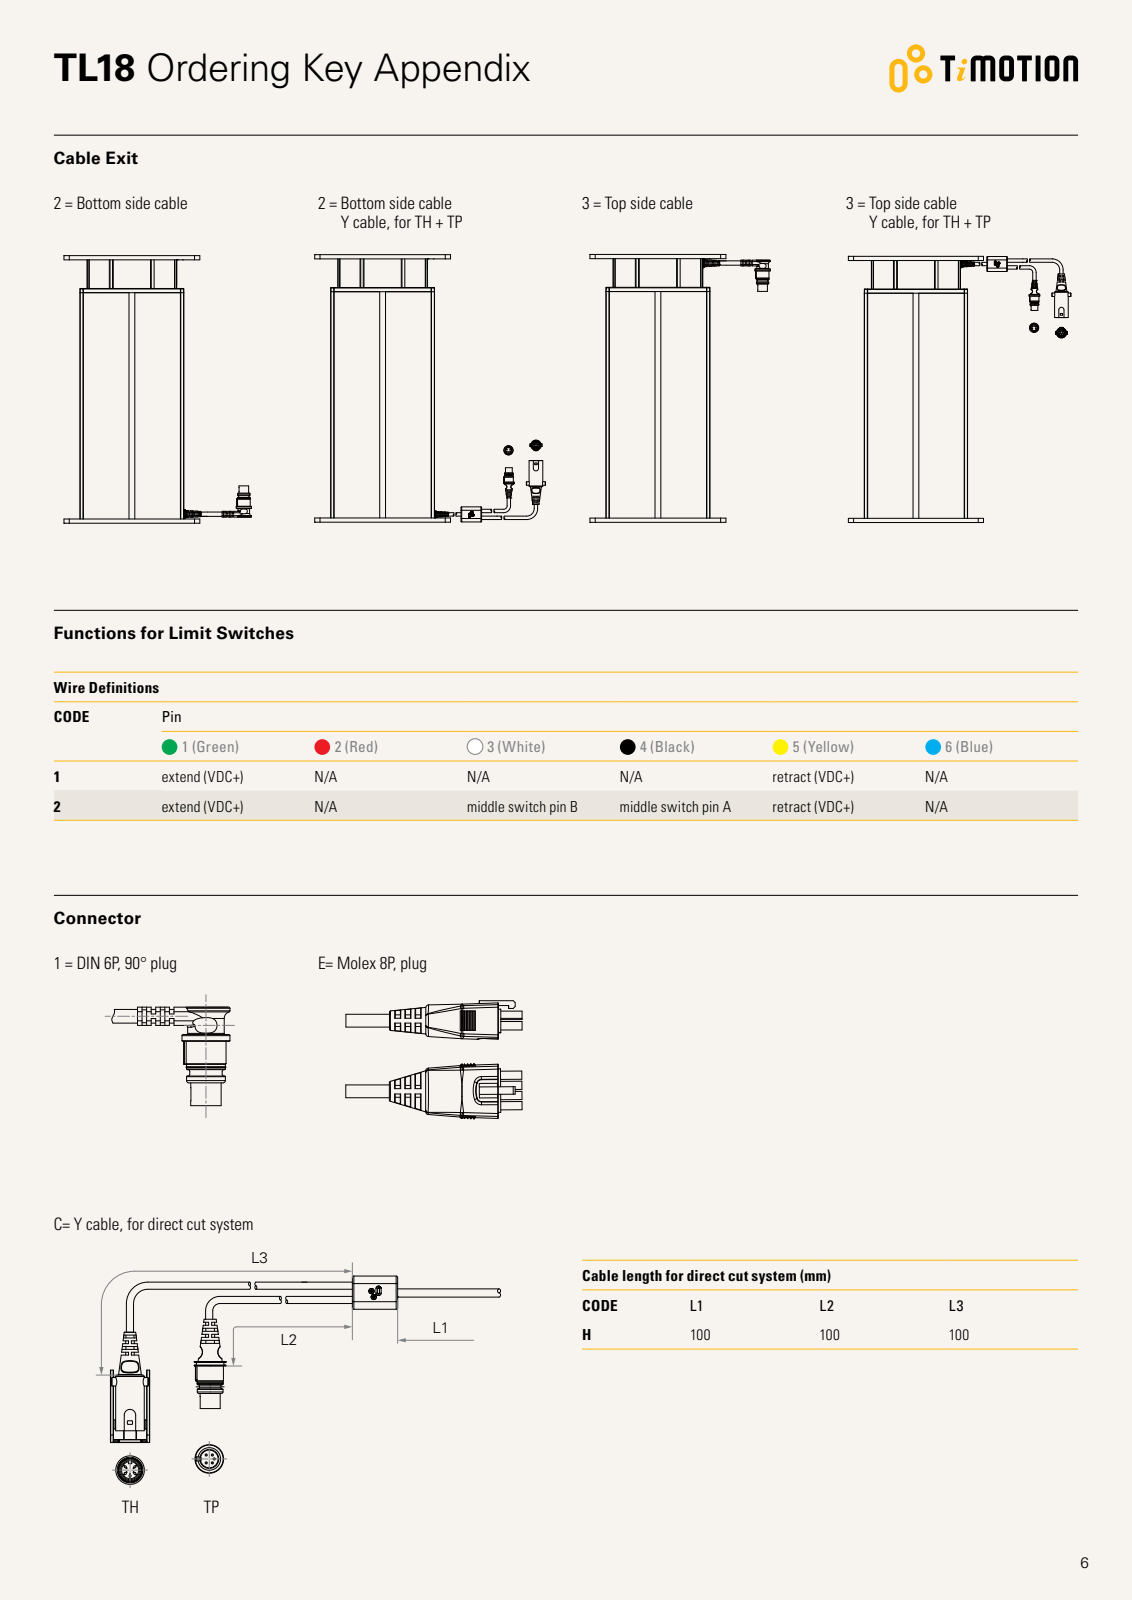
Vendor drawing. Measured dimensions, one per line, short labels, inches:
name: 3D_TL18
written by: SolidWorks 2015 (CONFIG_CONTROL_DESIGN)
unit: in
bodies: 1 solid, 731 faces (407 planar, 242 cylindrical, 82 other)
size: 26.378 × 10.118 × 7.677
volume: 1 159 in³; area: 1 155 in²
holes: 10× ⌀0.591, 8× ⌀0.236, 8× ⌀0.354, 8× ⌀0.374, 4× ⌀0.433, 2× ⌀0.165, 2× ⌀0.315
bosses: 5× ⌀0.583, 4× ⌀0.366
rounds: 24× R0.039, 16× R0.118, 4× R0.394
face distances: 5.843, 7.732, 0.315, 26.063, 0.394, 26.378, 7.339, 5.449, 0.236, 0.157
hole spacings: 0.669, 1.677, 0.64, 0.776, 0.946, 1.185, 1.21, 1.339
